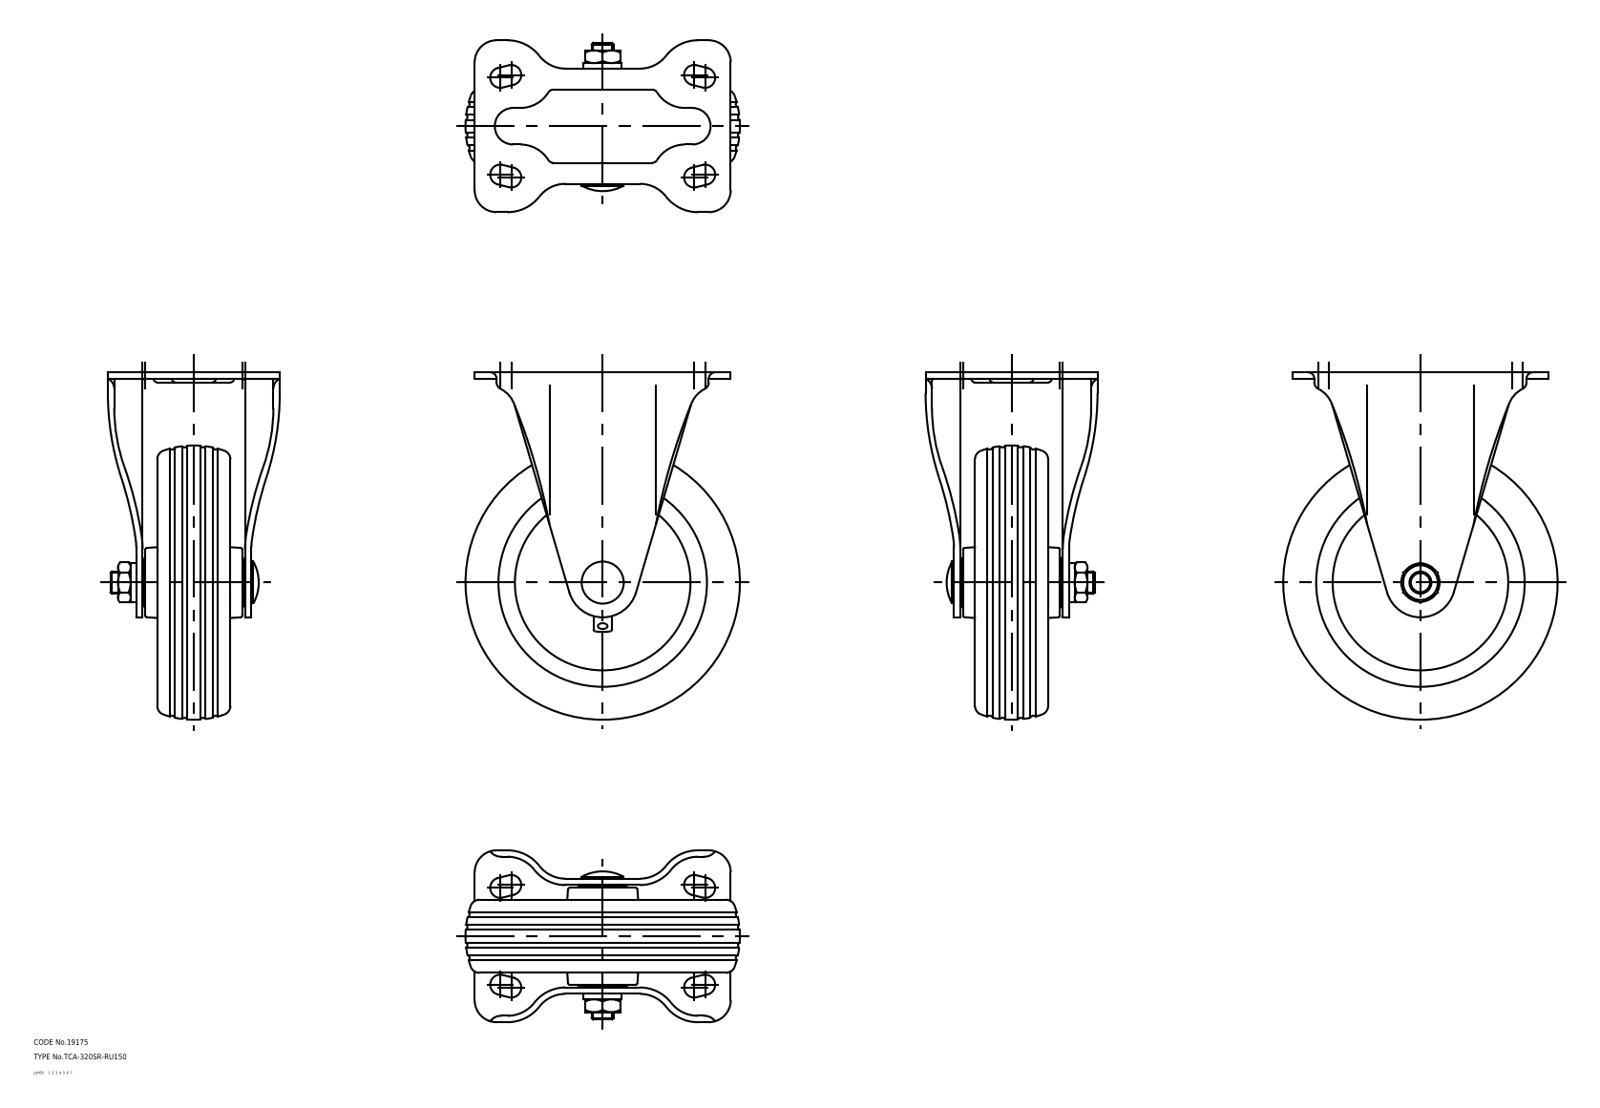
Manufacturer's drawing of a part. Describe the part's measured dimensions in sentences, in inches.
The part is named "67124351; 67124364; 67124377". Its 3-D file was written by "CADfix (AUTOMOTIVE_DESIGN)". It is 3 solids with 236 faces: 0 planar, 0 cylindrical and 236 other. Overall it measures 7.48 by 5.906 by 3.701 inches. Its volume is 42.48 cubic inches and its surface area 195.8 square inches.
